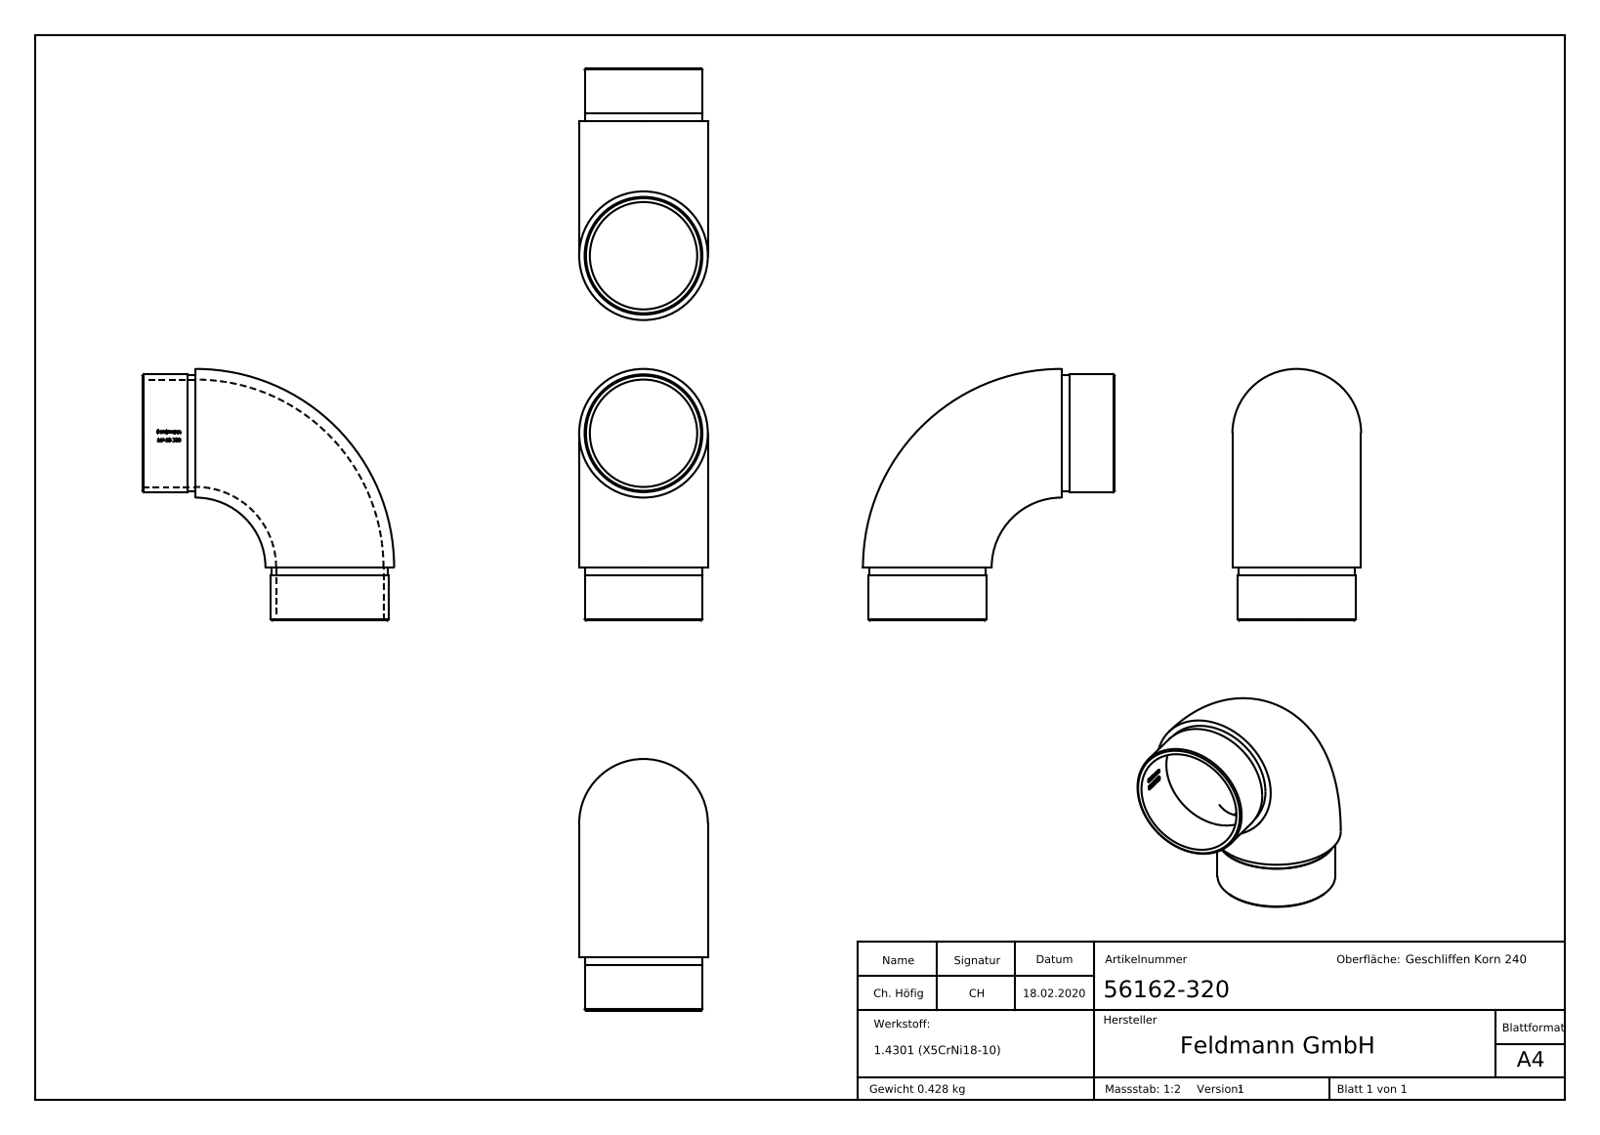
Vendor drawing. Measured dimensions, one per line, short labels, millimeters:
name: 56162-320
written by: SolidWorks 2015 (CONFIG_CONTROL_DESIGN)
unit: mm
bodies: 1 solid, 239 faces (97 planar, 29 cylindrical, 113 other)
size: 94.5 × 94.5 × 48.3
volume: 54 181 mm³; area: 33 777 mm²
holes: 2× ⌀40.3
bosses: 2× ⌀44.2, 2× ⌀43.8
rounds: 1× R20.25
face distances: 20, 17, 3, 0.39, 1.26, 2.97, 4.23, 1.32, 3.66, 3.27
